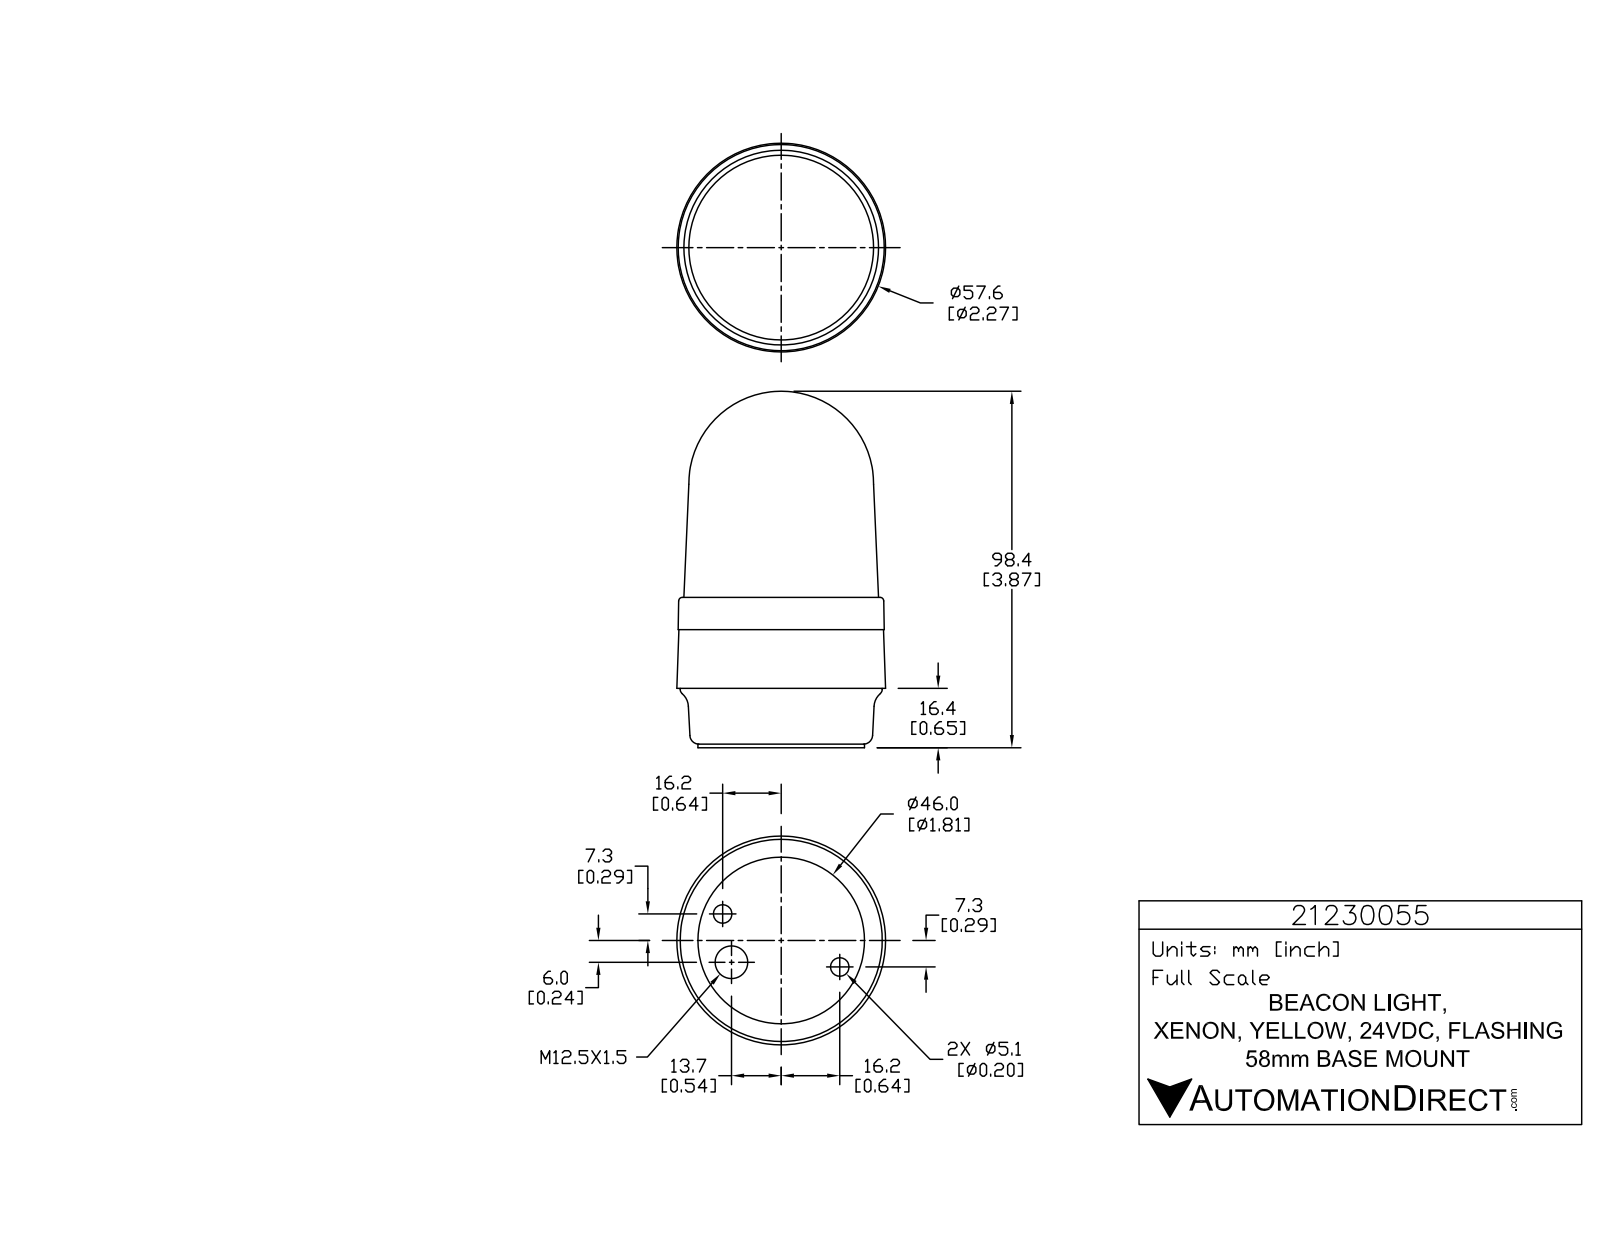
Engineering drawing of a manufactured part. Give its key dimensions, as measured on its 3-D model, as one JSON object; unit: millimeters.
{"part_name": "21230055", "step_written_by": "SolidWorks 2015 (AUTOMOTIVE_DESIGN)", "units": "millimeters", "bodies": {"solids": 1, "faces": 764, "planar": 527, "cylindrical": 145, "other": 92}, "overall_size": [98.4, 57.63, 57.63], "volume_mm3": 199898, "surface_area_mm2": 18922, "round_holes": [[0.99, 3], [5.11, 2], [9, 1]], "round_bosses_or_shafts": [[5.74, 3], [1.43, 3], [55.8, 1], [46, 1]], "partial_cylinders_radius": [[0.2, 6], [0.21, 6], [0.21, 6], [3.32, 6], [0.1, 3], [0.12, 3], [0.19, 3], [0.2, 3]], "face_to_face_distances": [16.4, 1, 15.4, 41.5, 40.5, 25.1, 32.6, 31.6, 16.2, 8.9], "hole_center_spacings": [13.56, 29.94, 35.5]}
